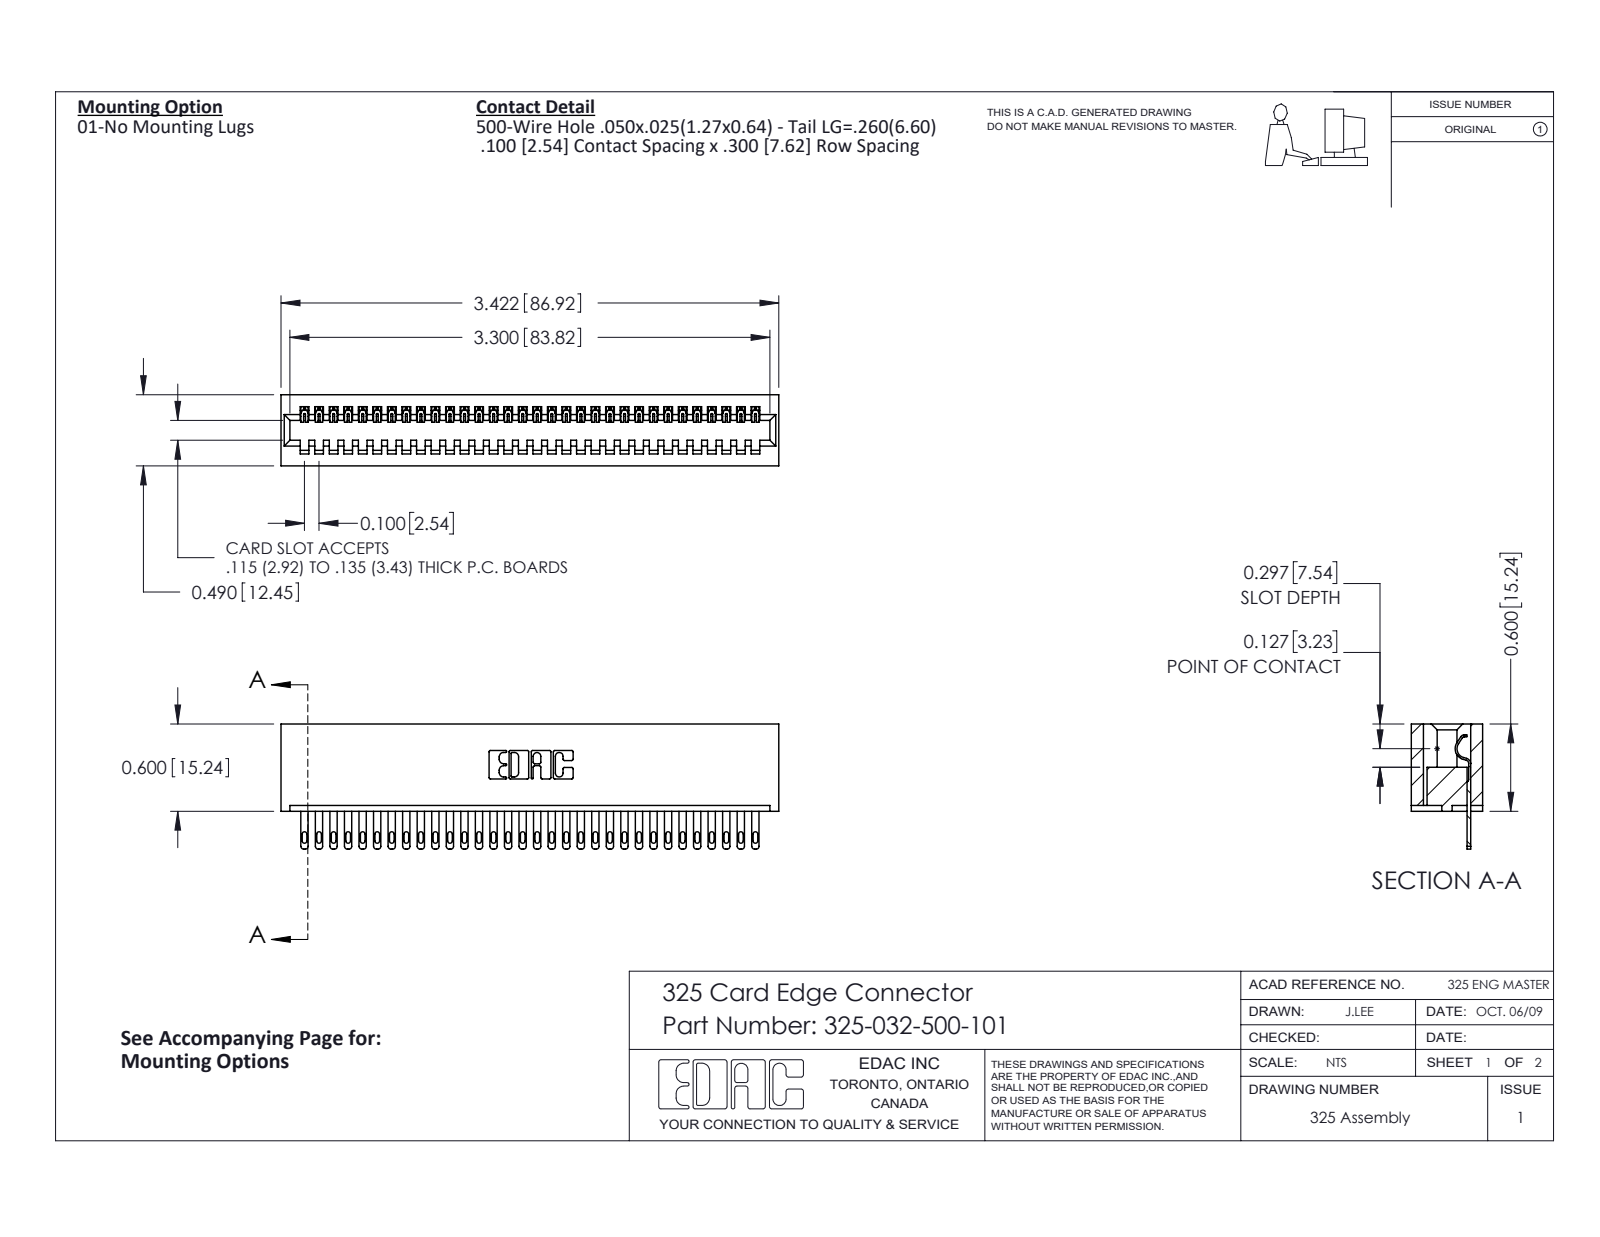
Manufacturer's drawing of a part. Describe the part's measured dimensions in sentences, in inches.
The part is named "325-032-500-101; 325 Part_Lugless; 325-292-001_325-293-100". Its 3-D file was written by "SolidWorks 2016 (CONFIG_CONTROL_DESIGN)". It is 33 solids with 1834 faces: 1218 planar, 616 cylindrical and 0 other. Overall it measures 3.422 by 0.86 by 0.49 inches. Its volume is 0.705 cubic inches and its surface area 20.17 square inches. Partial cylindrical surfaces (rounded edges, fillets, slot ends): 64 of radius 0.006, 64 of radius 0.016, 64 of radius 0.02, 22 of radius 0.01, 6 of radius 0.007, 6 of radius 0.031, 3 of radius 0.026, 1 of radius 0.014. The main face-to-face distances are 0.083, 0.407, 0.3, 0.49, 0.107, 0.383, 0.025, 0.325, 0.1, 0.2.
